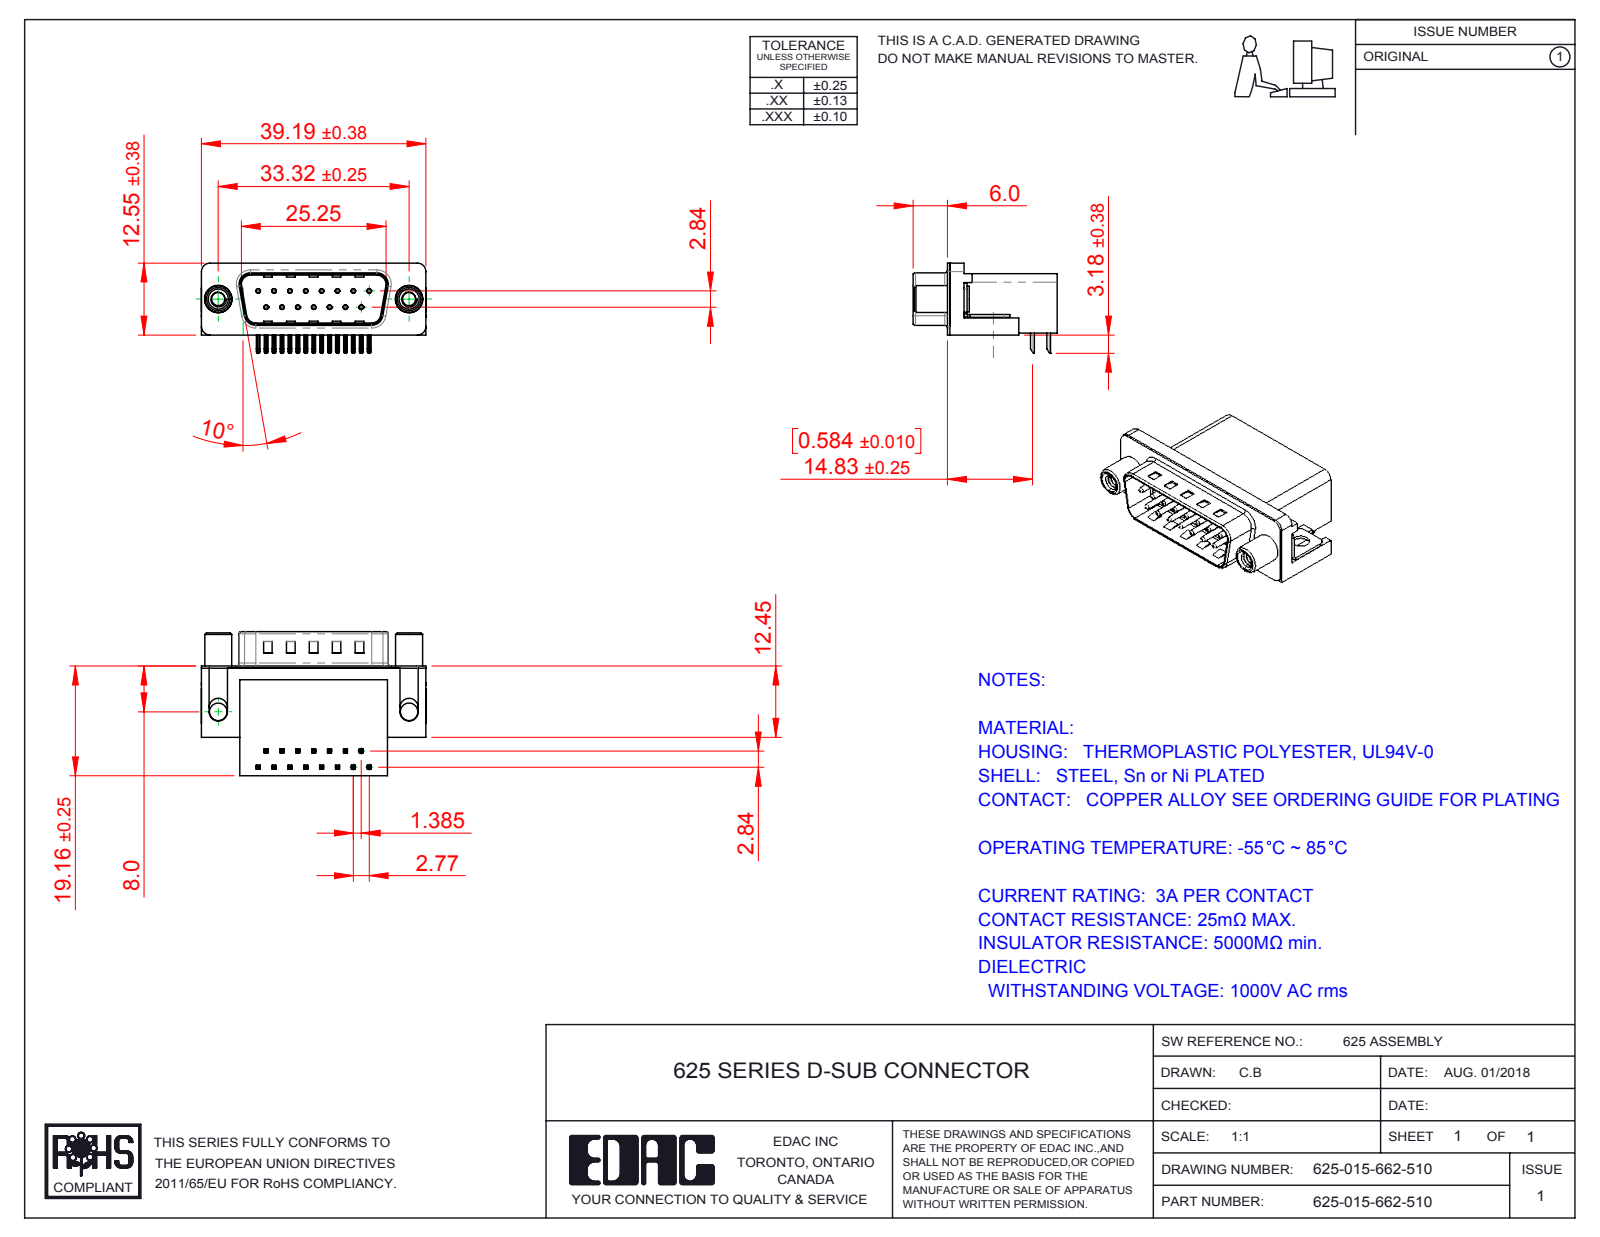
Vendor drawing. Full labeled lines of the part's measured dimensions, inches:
Part name (STEP PRODUCT): 625 Contact Bottom; 625 Contact Top; 625 Housing_15 Socket; 625 Round Threaded Standoff (+3 more)
STEP written by: SolidWorks 2016 (CONFIG_CONTROL_DESIGN)
Units: inches
Bodies: 21 solids, 1473 faces (885 planar, 455 cylindrical, 133 other)
Overall size (bounding box): 1.544 × 0.991 × 0.619
Volume: 0.386 in³ · Surface area: 10.25 in²
Round holes (diameter × count): ⌀0.014 ×15, ⌀0.031 ×15, ⌀0.091 ×2, ⌀0.12 ×2, ⌀0.122 ×2, ⌀0.157 ×2, ⌀0.189 ×2, ⌀0.197 ×2
Round bosses / shafts (diameter × count): ⌀0.03 ×15, ⌀0.193 ×2, ⌀0.185 ×2, ⌀0.177 ×2, ⌀0.152 ×2
Partial cylindrical surfaces — rounded edges, fillets, slot ends (radius × count): R0.01 ×60, R0.005 ×30, R0.039 ×16, R0.02 ×9, R0.063 ×8, R0.059 ×6, R0.035 ×4, R0.079 ×4
Main face-to-face distances: 0.016, 0.407, 0.739, 0.083, 0.412, 0.067, 0.428, 0.754, 0.345, 0.64
Hole centre spacings: 0.124, 0.109, 0.218, 0.327, 0.436, 0.198, 0.198, 0.294
